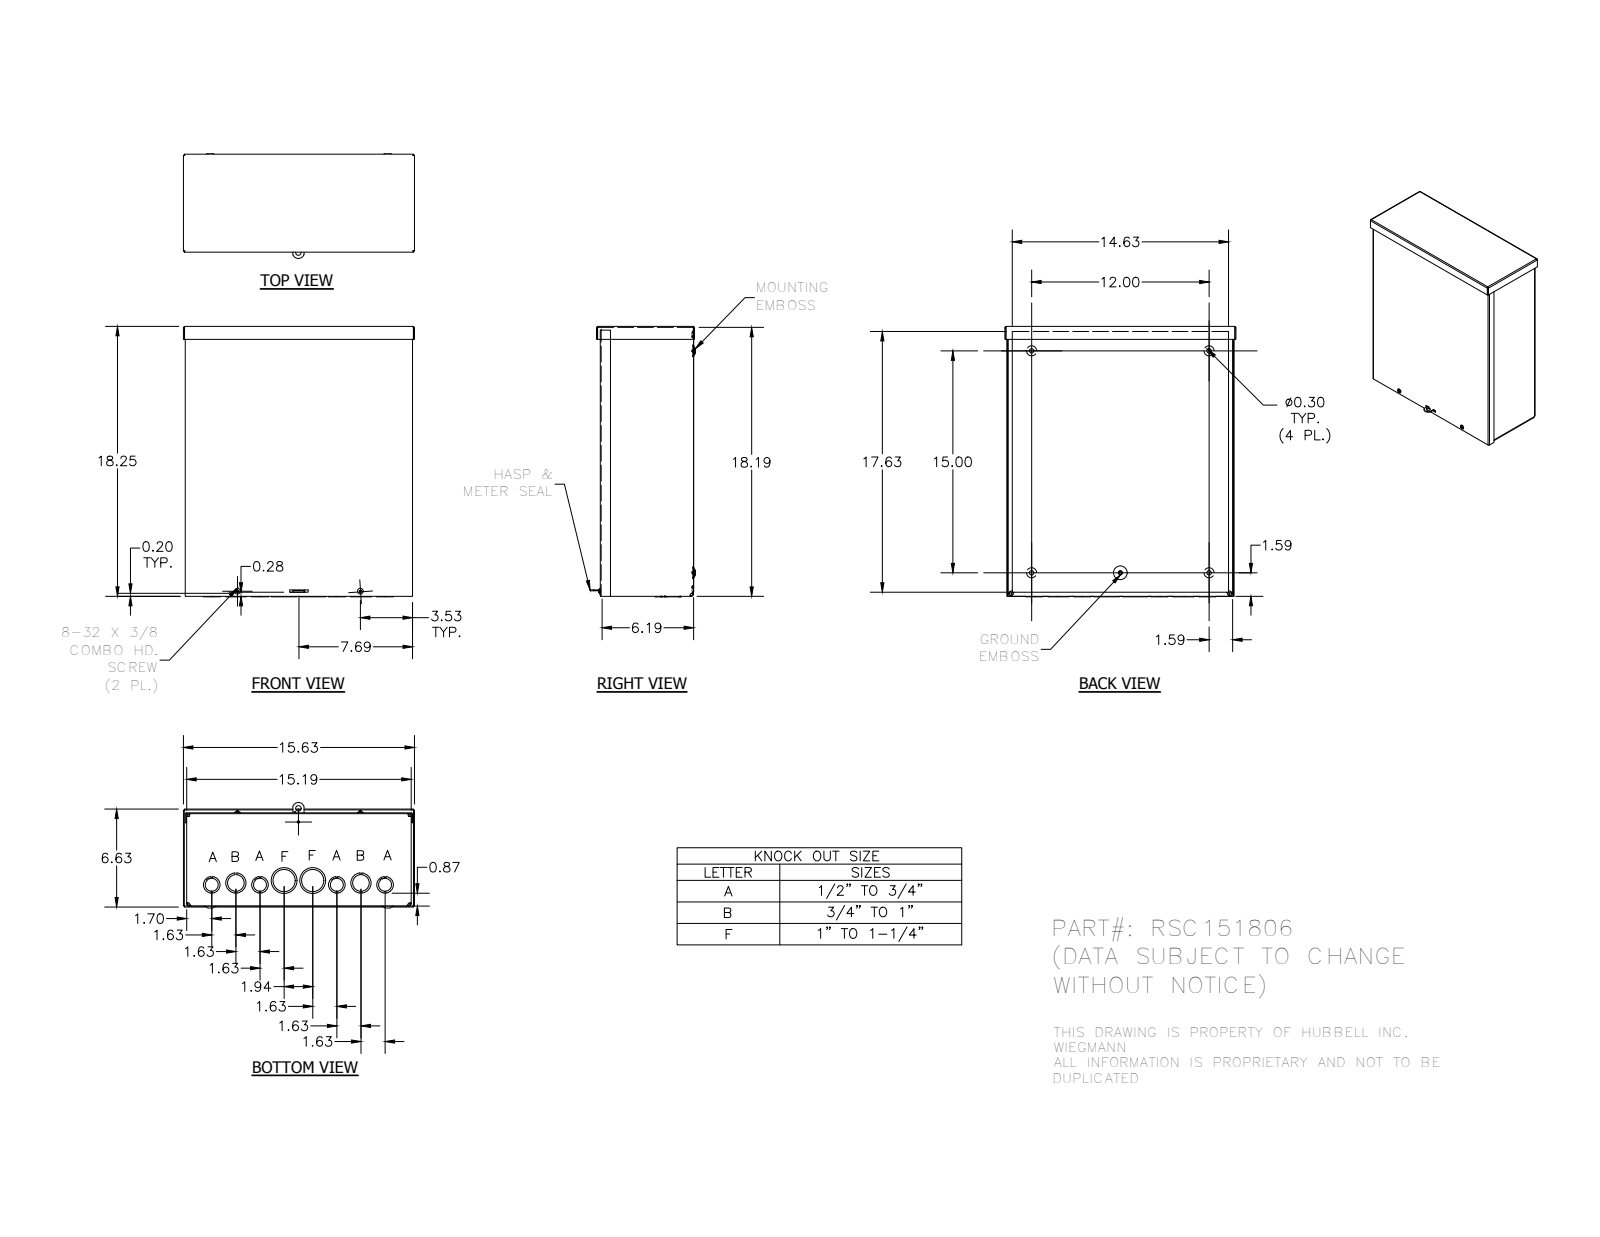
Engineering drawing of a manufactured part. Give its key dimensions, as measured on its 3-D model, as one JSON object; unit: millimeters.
{"part_name": "RSC151806G_WRAP; RSC1518G_LID; RSC1506G_CAP; 3183 (+4 more)", "step_written_by": "Autodesk Inventor 2014 (AUTOMOTIVE_DESIGN)", "units": "millimeters", "bodies": {"solids": 7, "faces": 619, "planar": 304, "cylindrical": 171, "other": 144}, "overall_size": [464.32, 396.88, 180.97], "volume_mm3": 1221000, "surface_area_mm2": 1565000, "round_holes": [[28.57, 6], [7.62, 4], [7.95, 4], [22.22, 4], [3.17, 2], [3.76, 2], [34.92, 2], [38.1, 2], [44.45, 2], [3.96, 1], [4.19, 1], [9.52, 1]], "round_bosses_or_shafts": [[9.75, 2], [4.17, 2], [5.8, 1]], "partial_cylinders_radius": [[0.25, 15], [0.79, 8], [2.37, 8], [3.17, 8], [4.75, 8], [0.79, 5], [0.53, 4], [1.4, 4]], "face_to_face_distances": [1.58, 158.73, 157.15, 1.59, 1.57, 160.32, 158.74, 384.19, 460.39, 3.15], "hole_center_spacings": [41.52, 214.88, 42.07, 82.8, 82.91, 90.99, 124.42, 126.18]}
